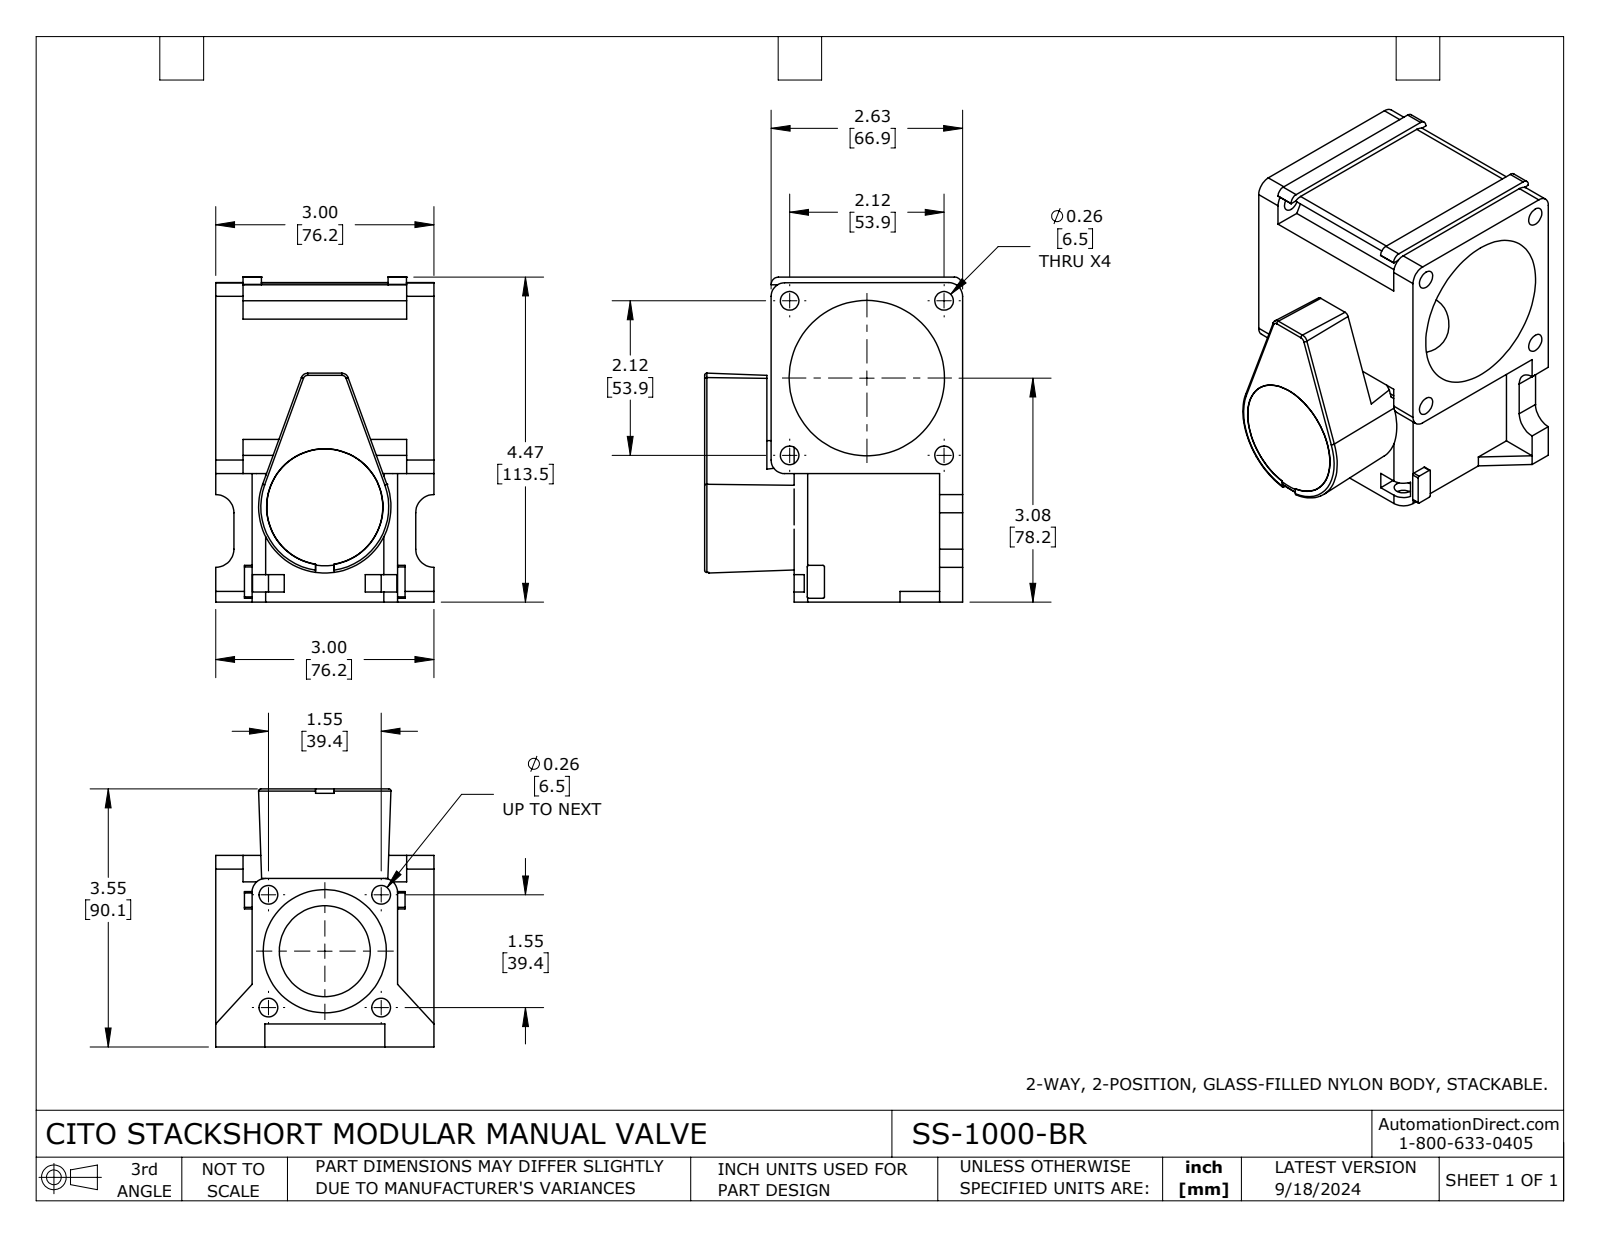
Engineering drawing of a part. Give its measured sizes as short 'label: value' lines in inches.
name: SS-1000-BR
written by: SolidWorks 2023 (CONFIG_CONTROL_DESIGN)
unit: in
bodies: 3 solids, 236 faces (127 planar, 93 cylindrical, 16 other)
size: 4.468 × 3.547 × 3
volume: 14.48 in³; area: 124.9 in²
holes: 4× ⌀0.256, 4× ⌀0.257, 1× ⌀0.52, 1× ⌀0.52, 1× ⌀1.08, 1× ⌀1.25, 1× ⌀1.284, 1× ⌀1.477, 1× ⌀1.484, 1× ⌀1.595, 1× ⌀1.693, 1× ⌀2.136
bosses: 1× ⌀1.6
rounds: 6× R0.02, 4× R0.25, 3× R0.03, 3× R0.187, 2× R0.01, 2× R0.1, 2× R0.819, 1× R0.187
face distances: 2.5, 0.5, 2.632, 0.316, 2.316, 2, 0.915, 3.231, 3.547, 3
hole spacings: 1.502, 2.124, 1.096, 1.096, 1.55, 1.55, 2.192, 3.003
